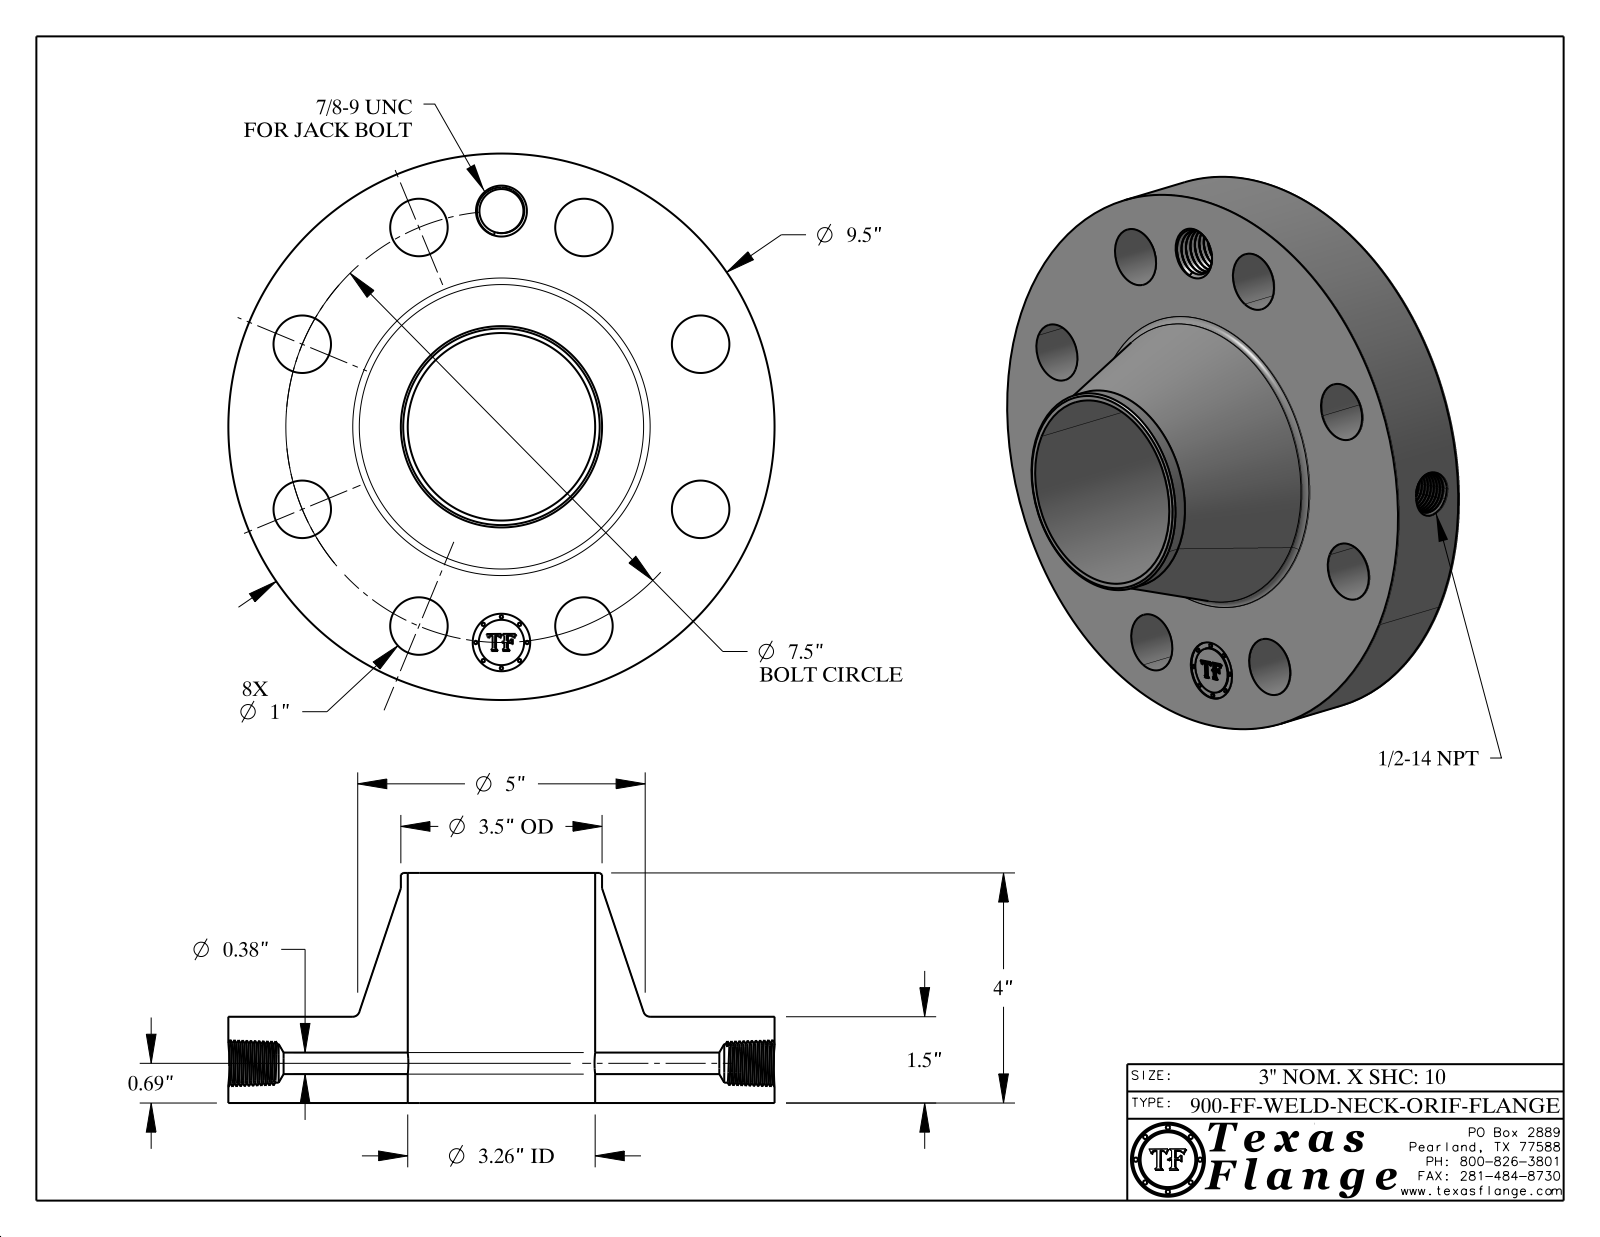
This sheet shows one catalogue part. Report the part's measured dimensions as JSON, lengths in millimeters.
{"part_name": "900-FF-WELD-NECK", "step_written_by": "CATIA V5 STEP AP214 (AUTOMOTIVE_DESIGN)", "units": "millimeters", "bodies": {"solids": 1, "faces": 756, "planar": 368, "cylindrical": 88, "other": 300}, "overall_size": [241.3, 241.3, 101.6], "volume_mm3": 1574000, "surface_area_mm2": 178000, "round_holes": [[25.4, 9], [9.5, 1], [17.1, 1], [19.5, 1], [82.8, 1]], "round_bosses_or_shafts": [[1.5, 8], [241.3, 1], [88.9, 1], [20, 1]], "face_to_face_distances": [38.1, 101.6, 63.5, 37.7, 0.4, 63.9, 7.6, 7.4, 1.4, 6.3], "hole_center_spacings": [95.3, 72.9, 134.7, 176, 190.5, 37.2, 105.8, 158.4]}
